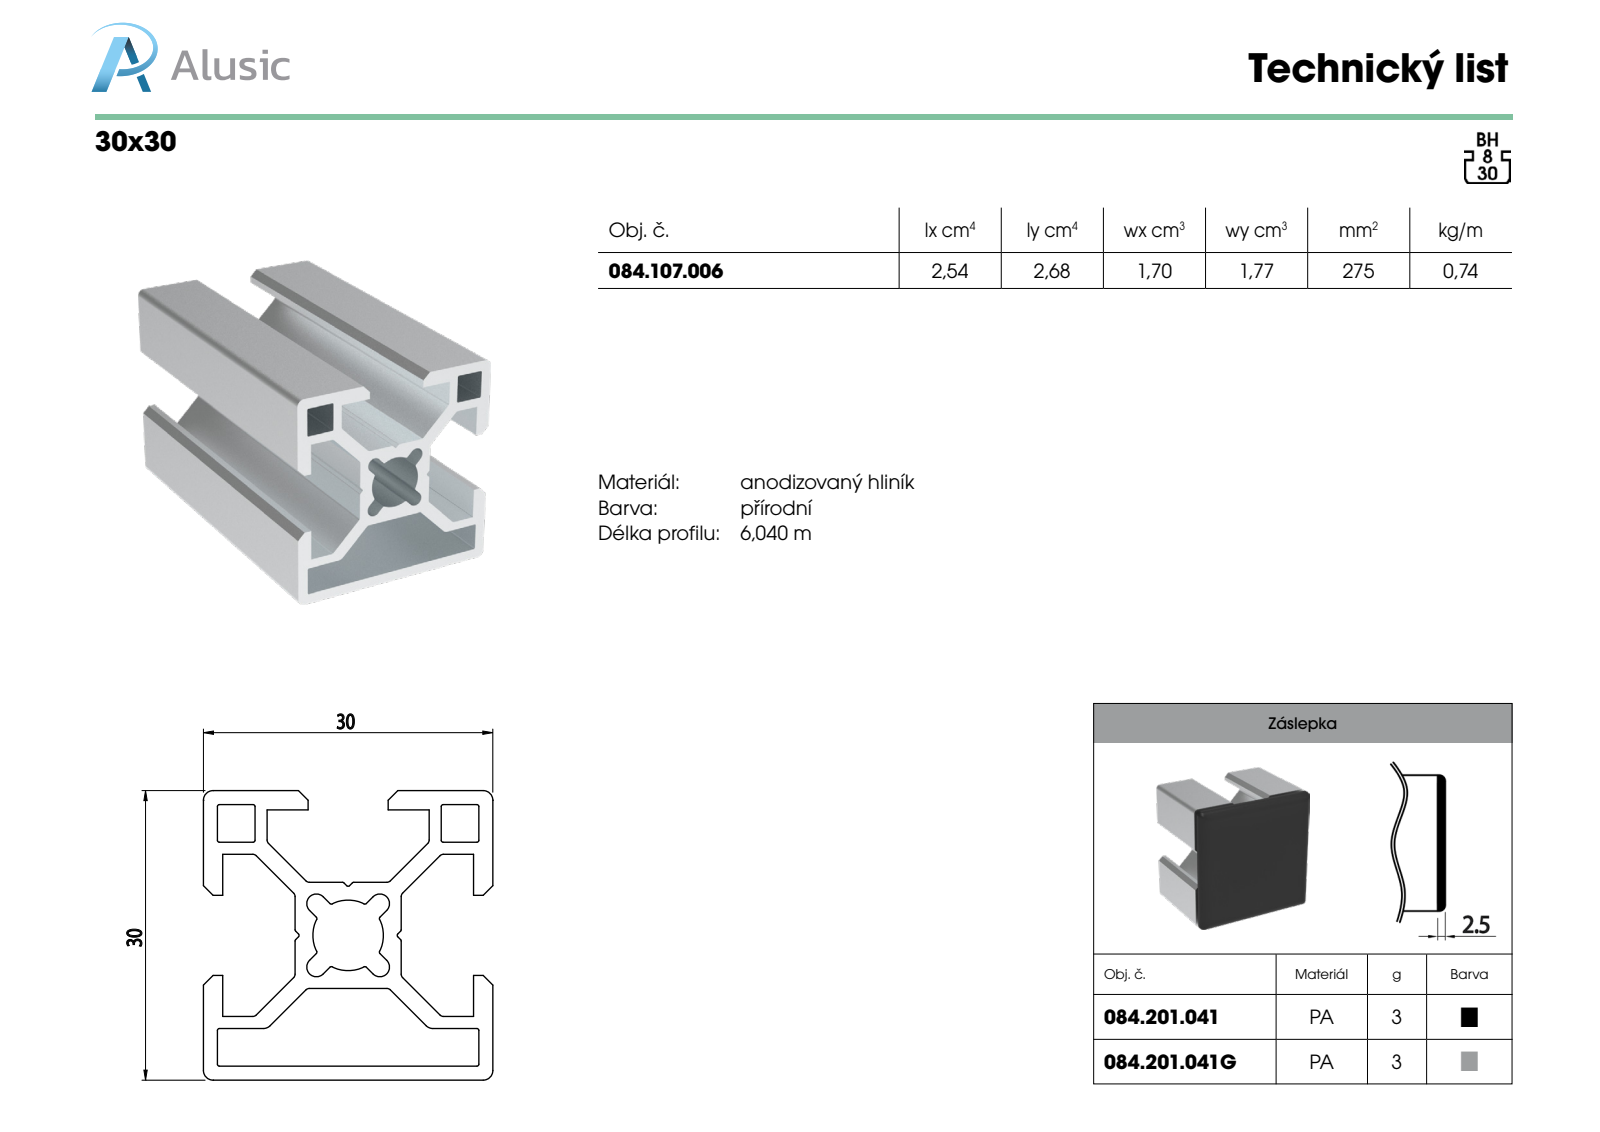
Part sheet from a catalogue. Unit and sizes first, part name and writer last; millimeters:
Units: millimetres
Overall size (bounding box): 100 × 30 × 30
Partial cylindrical surfaces — rounded edges, fillets, slot ends (radius × count): R0.2 ×29, R0.5 ×14, R1 ×10, R3.65 ×1
Main face-to-face distances: 1.45, 28.55, 30, 2, 20.5, 9.5, 8.05, 19.05, 28, 5.35
Volume: 27 503 mm³ · Surface area: 34 594 mm²
Bodies: 1 solid, 138 faces (75 planar, 63 cylindrical, 0 other)
Part name (STEP PRODUCT): 084.107.006
STEP written by: SolidWorks 2018 (AUTOMOTIVE_DESIGN)
